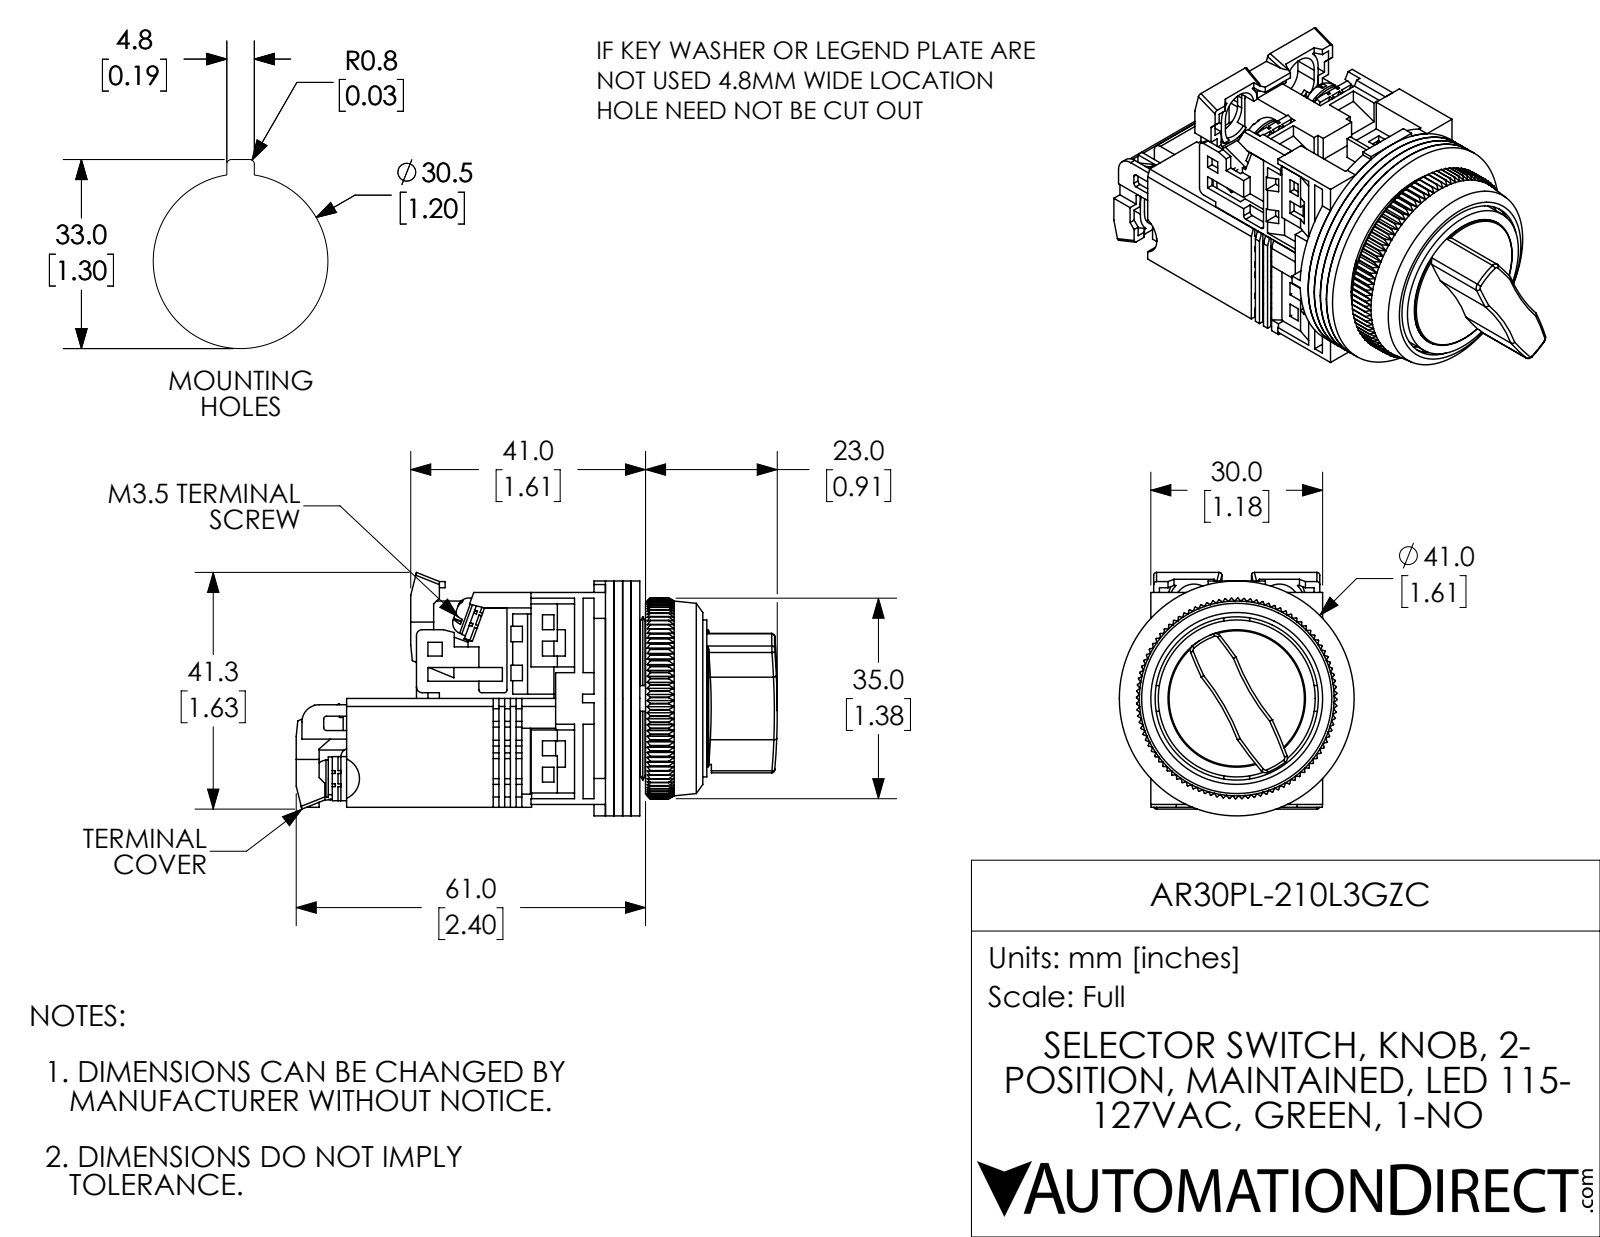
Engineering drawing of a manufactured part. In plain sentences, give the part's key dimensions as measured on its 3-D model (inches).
The part is named "AR30PL-210L3GZC". Its 3-D file was written by "SolidWorks 2017 (AUTOMOTIVE_DESIGN)". It is 27 solids with 2357 faces: 1706 planar, 321 cylindrical and 330 other. Overall it measures 3.307 by 1.673 by 1.614 inches. Its volume is 3.001 cubic inches and its surface area 63.38 square inches. Round holes: 6 of diameter 0.138, 4 of diameter 0.142, 3 of diameter 0.118, 1 of diameter 0.472, 1 of diameter 0.709, 1 of diameter 0.768, 1 of diameter 0.827, 1 of diameter 1.122, 1 of diameter 1.181, 1 of diameter 1.252. Round bosses or shafts: 4 of diameter 0.26, 2 of diameter 0.138, 2 of diameter 0.063, 1 of diameter 1.614, 1 of diameter 1.15, 1 of diameter 1.079, 1 of diameter 0.945, 1 of diameter 0.886. Partial cylindrical surfaces (rounded edges, fillets, slot ends): 17 of radius 0.059, 13 of radius 0.02, 6 of radius 0.039, 4 of radius 0.138, 4 of radius 0.177, 2 of radius 0.118, 2 of radius 1.575, 2 of radius 2.953. The main face-to-face distances are 0.059, 0.118, 0.177, 0.079, 0.039, 0.748, 0.787, 0.197, 0.256, 1.417. The hole center spacings are 0.579, 0.297, 0.624, 0.02, 0.302, 0.583, 0.583, 0.606.
